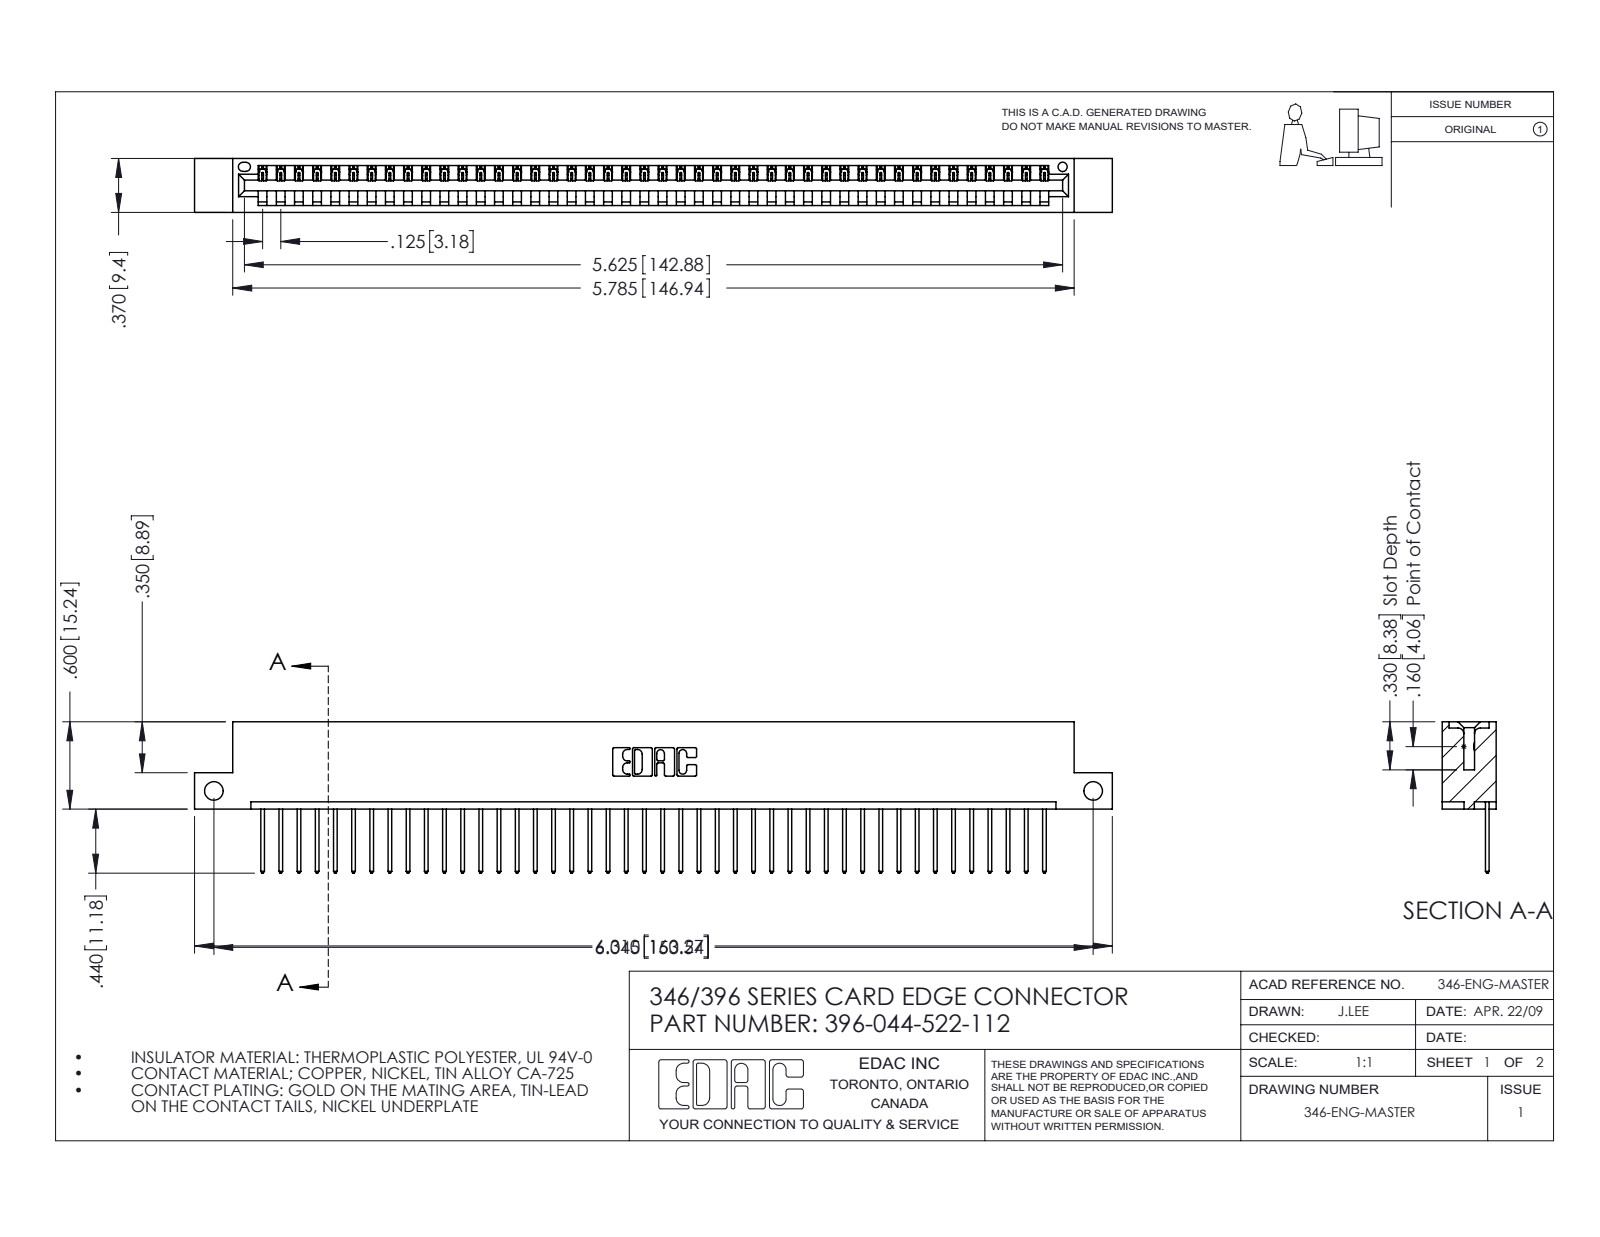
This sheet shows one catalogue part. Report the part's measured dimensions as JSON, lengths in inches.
{"part_name": "396-044-522-112; 346 Part_Flush Mounting Lugs - Side Mount; 345-292-001_345-293-122", "step_written_by": "SolidWorks 2016 (CONFIG_CONTROL_DESIGN)", "units": "inches", "bodies": {"solids": 45, "faces": 2674, "planar": 1836, "cylindrical": 838, "other": 0}, "overall_size": [6.31, 1.04, 0.37], "volume_in3": 0.932, "surface_area_in2": 29.65, "round_holes": [[0.128, 2], [0.064, 1]], "partial_cylinders_radius": [[0.006, 88], [0.01, 88], [0.01, 22], [0.007, 6], [0.031, 6], [0.026, 3], [0.031, 2], [0.04, 2]], "face_to_face_distances": [0.048, 0.322, 0.37, 0.25, 0.072, 0.298, 0.025, 0.148, 0.222, 0.1], "hole_center_spacings": [6.045]}
